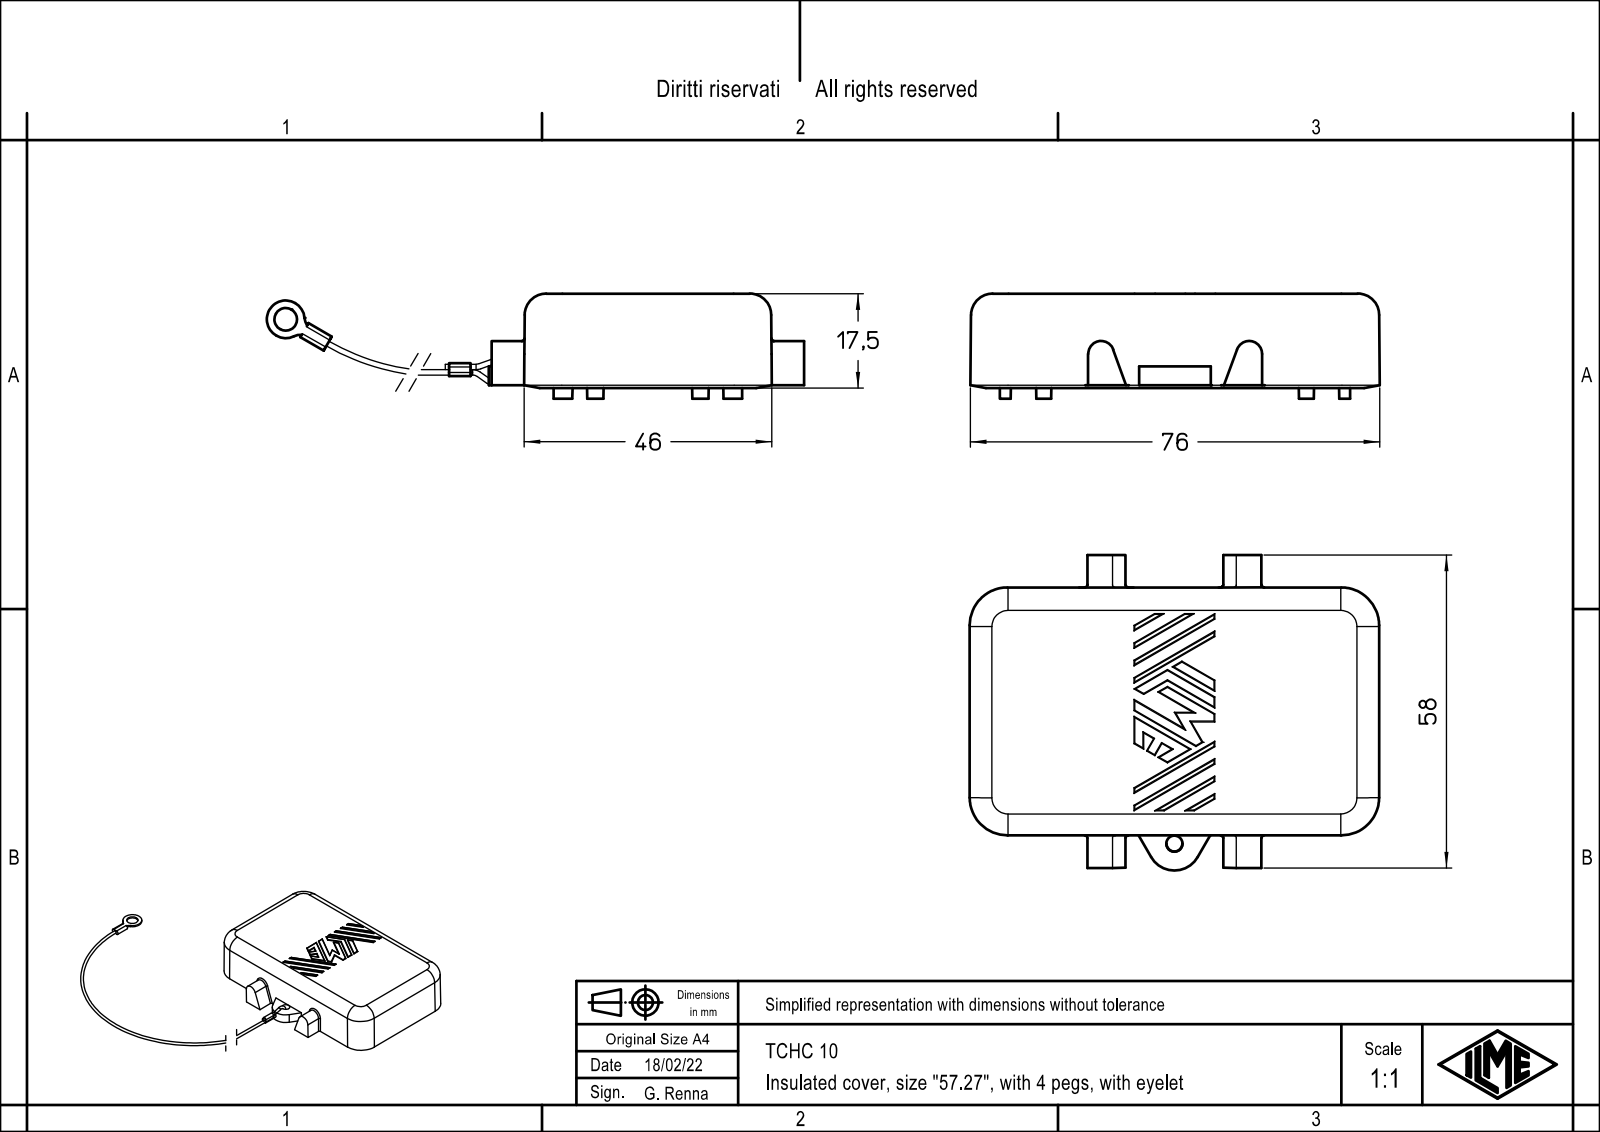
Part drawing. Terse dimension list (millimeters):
name: TCHC_10
written by: Creo Elements/Direct Modeling 20.1B 02-Apr-2019 (C) Parametric Technology GmbH (AUTOMOTIVE_DESIGN)
unit: mm
bodies: 1 solid, 277 faces (116 planar, 122 cylindrical, 39 other)
size: 228.27 × 88 × 19.65
volume: 34 203 mm³; area: 15 086 mm²
holes: 1× ⌀3, 1× ⌀4.2
bosses: 4× ⌀1, 1× ⌀7
rounds: 44× R0.15, 8× R1.5, 4× R0.5, 4× R4, 4× R7, 2× R0.7, 2× R0.75, 2× R1.25
face distances: 5.5, 11.49, 16.99, 17.14, 5.65, 7, 6.99, 58, 19.5, 12.22
hole spacings: 130.24
